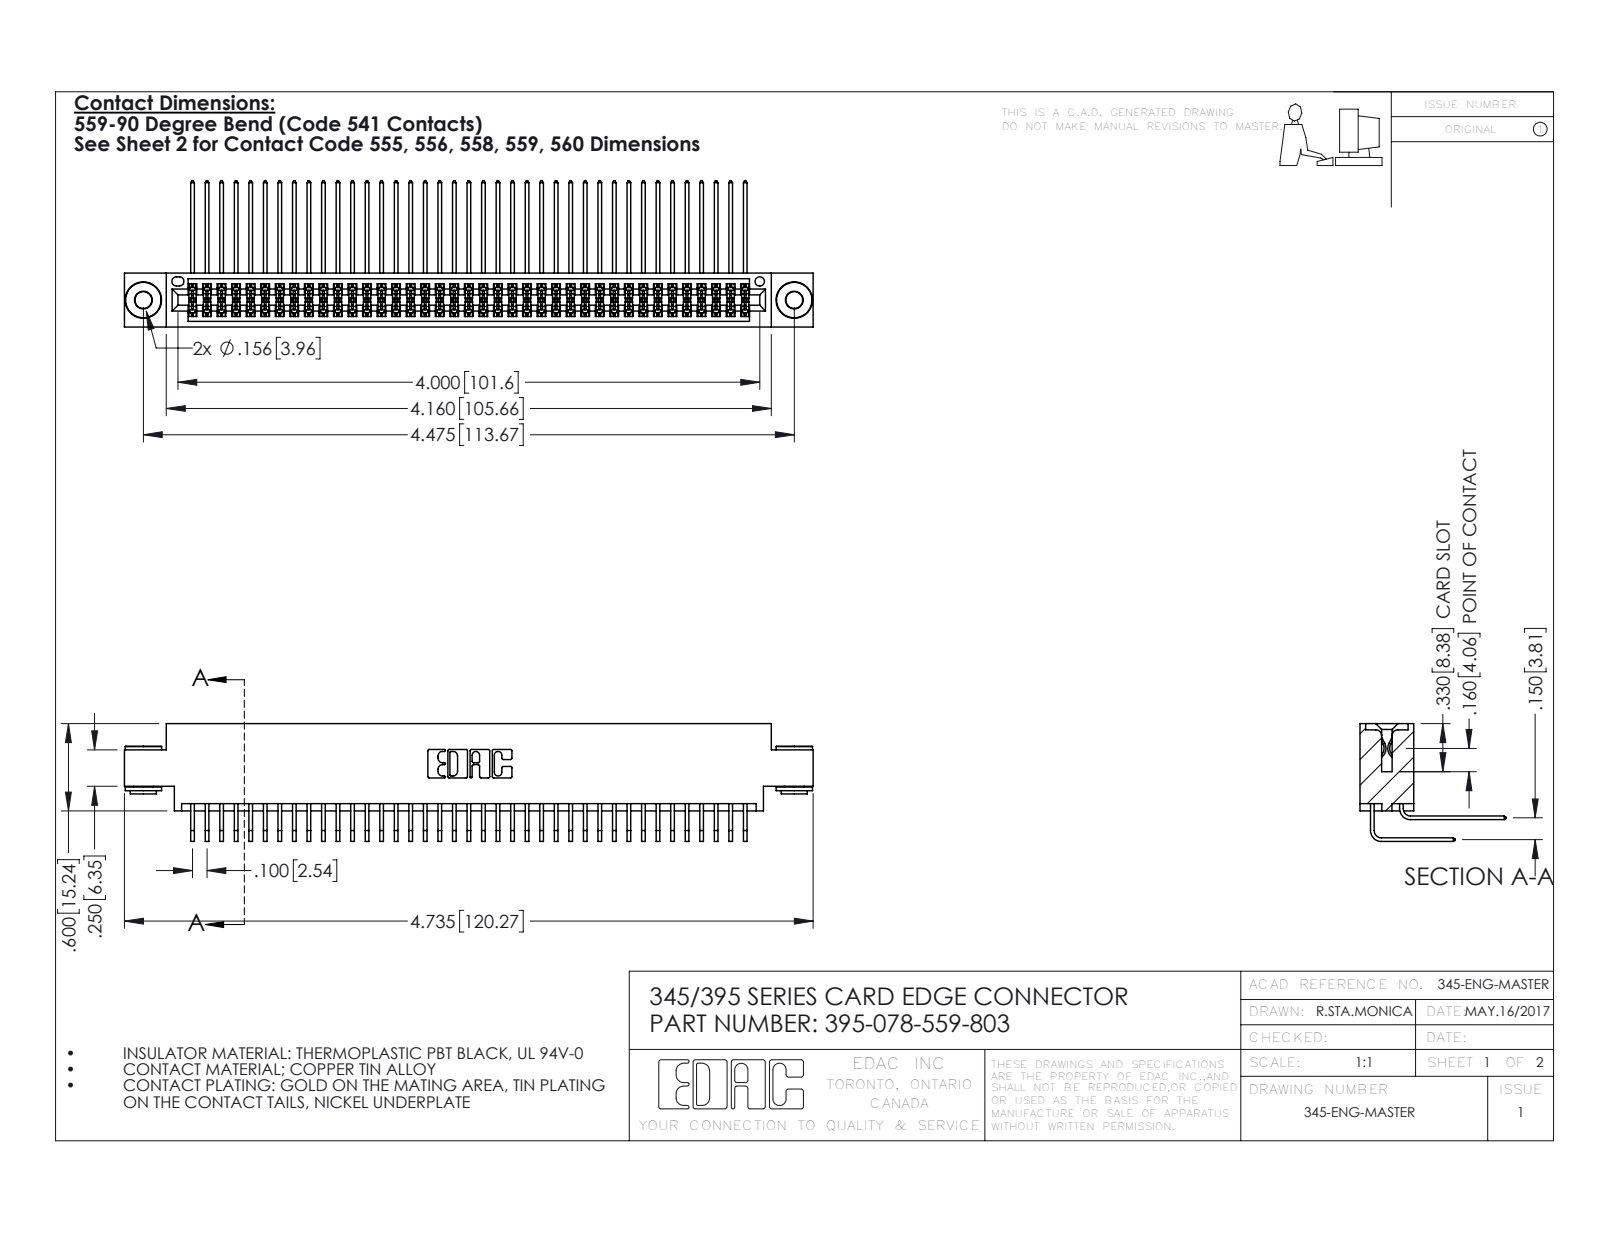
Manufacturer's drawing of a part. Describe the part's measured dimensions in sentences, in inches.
The part is named "395-078-559-803; 345-250-002_345-250-002-102; 345-292-001_558 559 Tail - 1; 345-292-001_559 Tail - 2 (+1 more)". Its 3-D file was written by "SolidWorks 2016 (CONFIG_CONTROL_DESIGN)". It is 81 solids with 4224 faces: 2824 planar, 1392 cylindrical and 8 other. Overall it measures 4.735 by 1.005 by 0.809 inches. Its volume is 0.733 cubic inches and its surface area 31.25 square inches. Round holes: 2 of diameter 0.116, 2 of diameter 0.156, 1 of diameter 0.064. Round bosses or shafts: 2 of diameter 0.25, 2 of diameter 0.18, 2 of diameter 0.136. Partial cylindrical surfaces (rounded edges, fillets, slot ends): 117 of radius 0.006, 22 of radius 0.01, 6 of radius 0.007, 6 of radius 0.031, 3 of radius 0.026, 2 of radius 0.014, 2 of radius 0.019, 2 of radius 0.022. The main face-to-face distances are 0.072, 0.298, 0.37, 0.2, 0.098, 0.272, 0.025, 0.175, 0.225, 0.15. The hole center spacings are 0.27, 4.239, 4.475.
